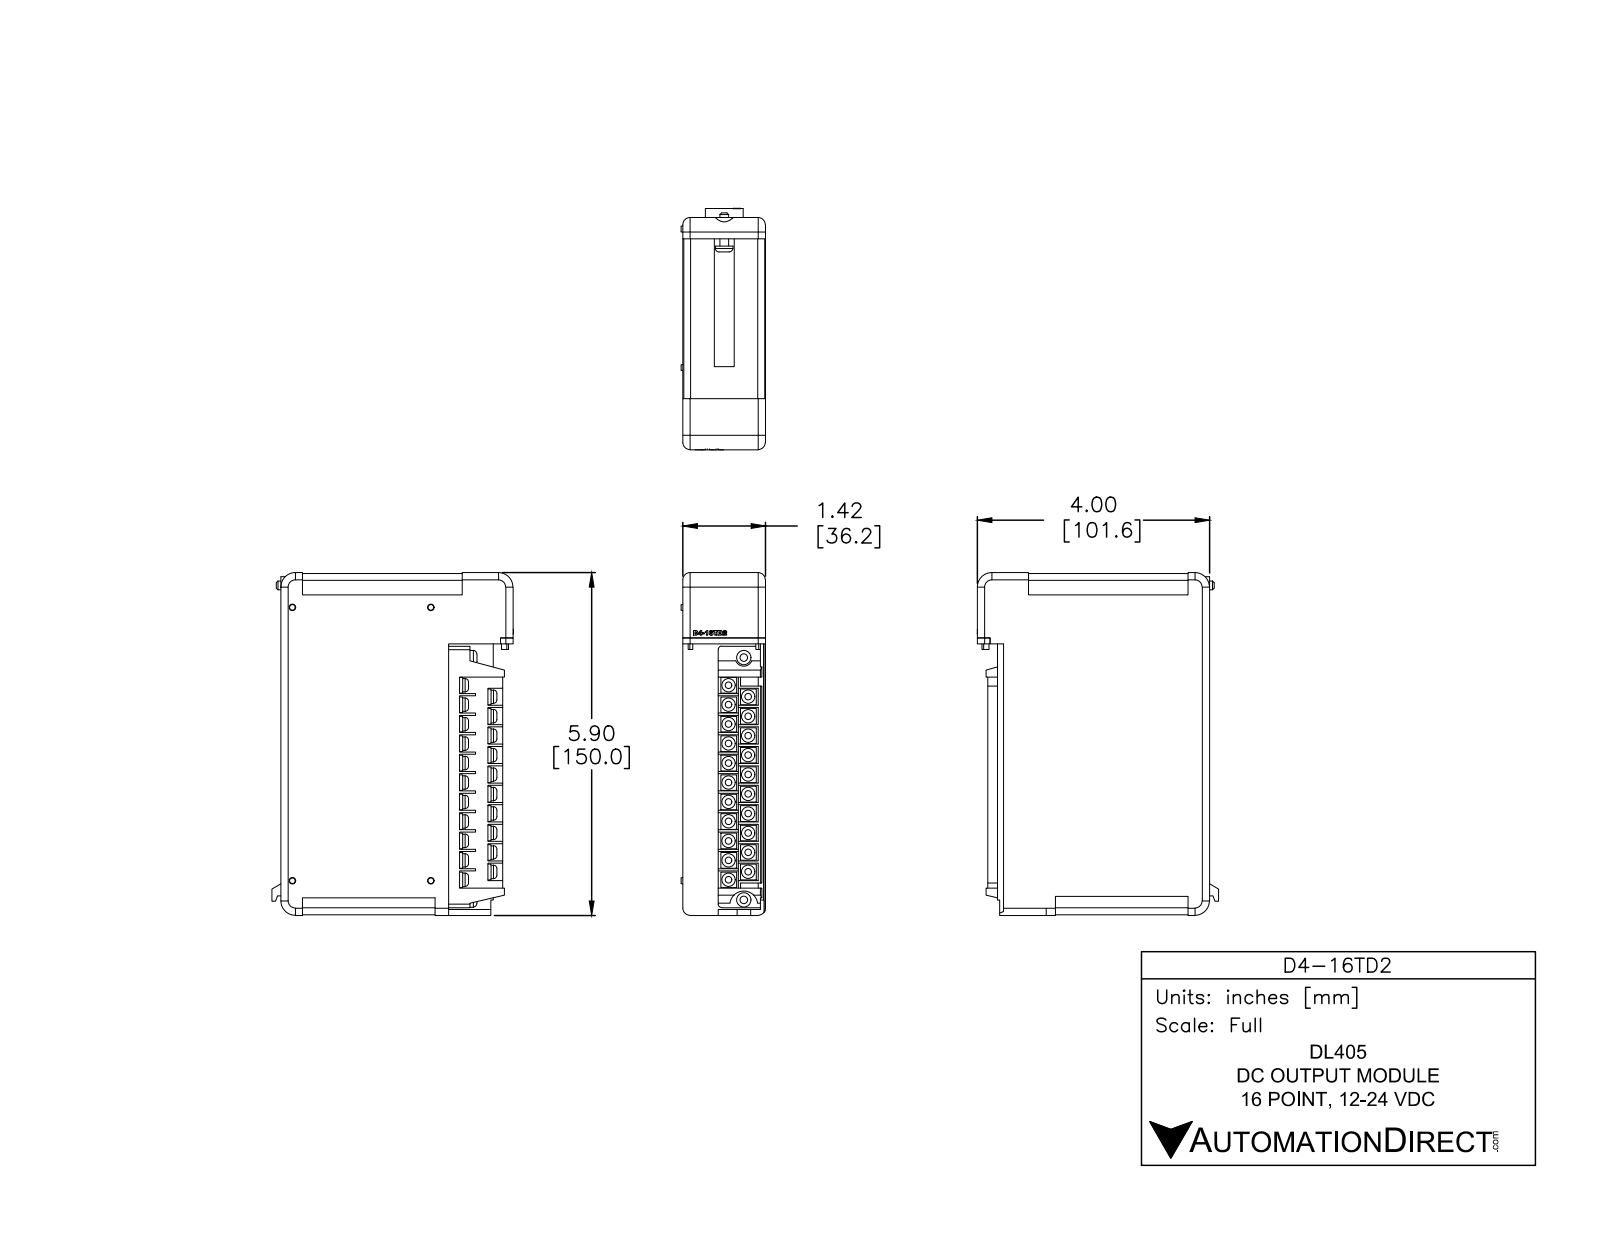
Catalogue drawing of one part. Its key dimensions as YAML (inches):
part_name: "D4-16TD2"
step_written_by: "SolidWorks 2014 (AUTOMOTIVE_DESIGN)"
units: inches
bodies: {solids: 14, faces: 599, planar: 412, cylindrical: 86, other: 101}
overall_size: [5.905, 4.156, 1.455]
volume: 27.51
surface_area: 86.82
round_bosses_or_shafts:
  - {diameter: 0.23, count: 21}
  - {diameter: 0.25, count: 2}
  - {diameter: 0.3, count: 1}
  - {diameter: 0.15, count: 1}
partial_cylinders:
  - {radius: 0.125, count: 8}
  - {radius: 0.12, count: 4}
  - {radius: 0.25, count: 3}
  - {radius: 0.015, count: 2}
  - {radius: 0.03, count: 2}
  - {radius: 0.06, count: 2}
  - {radius: 0.149, count: 1}
  - {radius: 0.151, count: 1}
face_to_face_distances: [1.425, 0.015, 2.89, 5.875, 1.41, 0.47, 0.2, 0.955, 5.89, 1.21]
